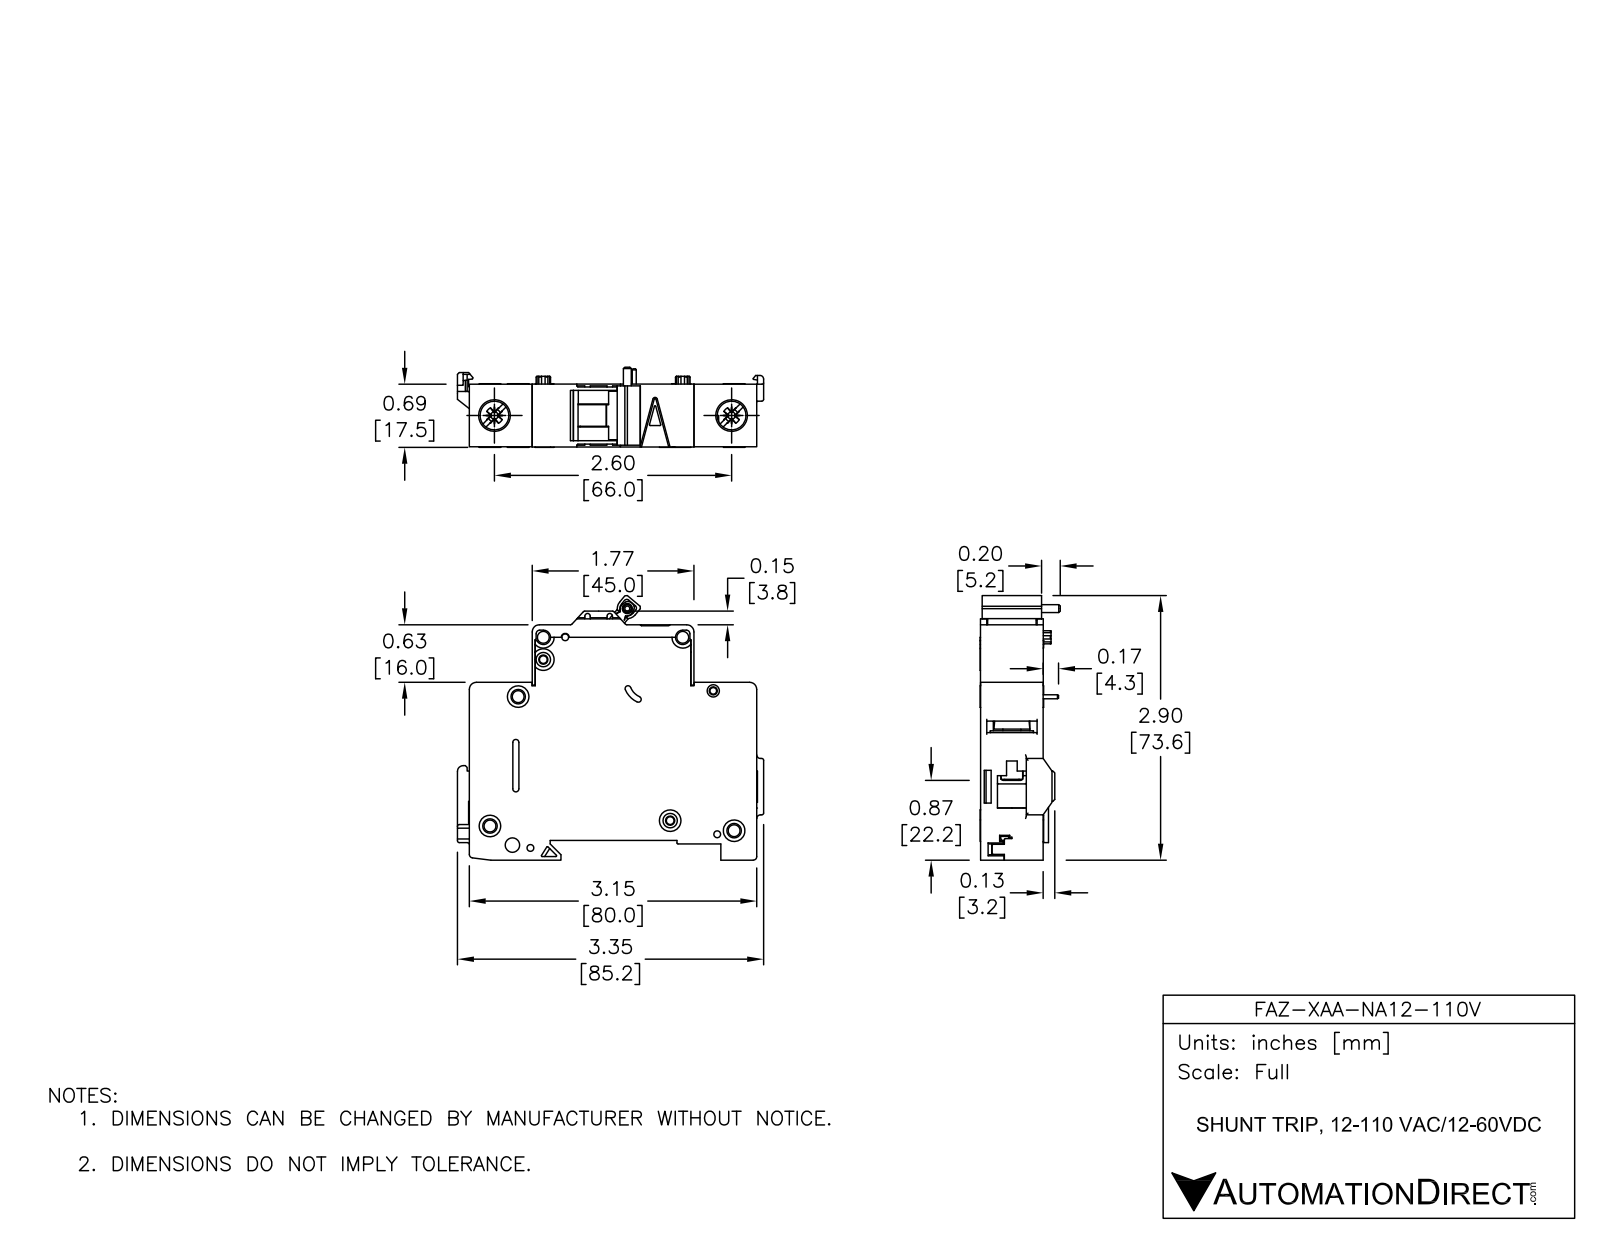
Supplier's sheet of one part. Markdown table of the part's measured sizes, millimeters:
| quantity | value |
| --- | --- |
| part name | FAZ-XAA-NA12-110 |
| STEP written by | SolidWorks 2014 (AUTOMOTIVE_DESIGN) |
| units | millimeters |
| bodies | 3 solids, 826 faces (406 planar, 288 cylindrical, 132 other) |
| overall size | 105 × 73.04 × 24.7 |
| volume | 77 757 mm³ |
| surface area | 24 729 mm² |
| round holes (diameter × count) | 3.6 × 5, 1.09 × 2, 1.5 × 2, 2.4 × 2, 4 × 2, 7.15 × 2, 8.2 × 2, 1.9 × 1, 2.15 × 1, 2.2 × 1, 2.55 × 1, 3.3 × 1 |
| round bosses / shafts (diameter × count) | 6 × 6, 3.6 × 2, 2.5 × 1, 1.1 × 1 |
| partial cylindrical surfaces (radius × count) | 0.5 × 30, 0.25 × 29, 1 × 12, 2 × 10, 5 × 5, 4 × 4, 1.8 × 3, 0.2 × 2 |
| main face-to-face distances | 17.5, 15.05, 0.7, 2.45, 1.75, 15.75, 13.3, 14, 12.6, 2 |
| hole center spacings | 6.2, 5.19, 6.1, 8.19, 8.56, 8.7, 11.11, 12.45 |
